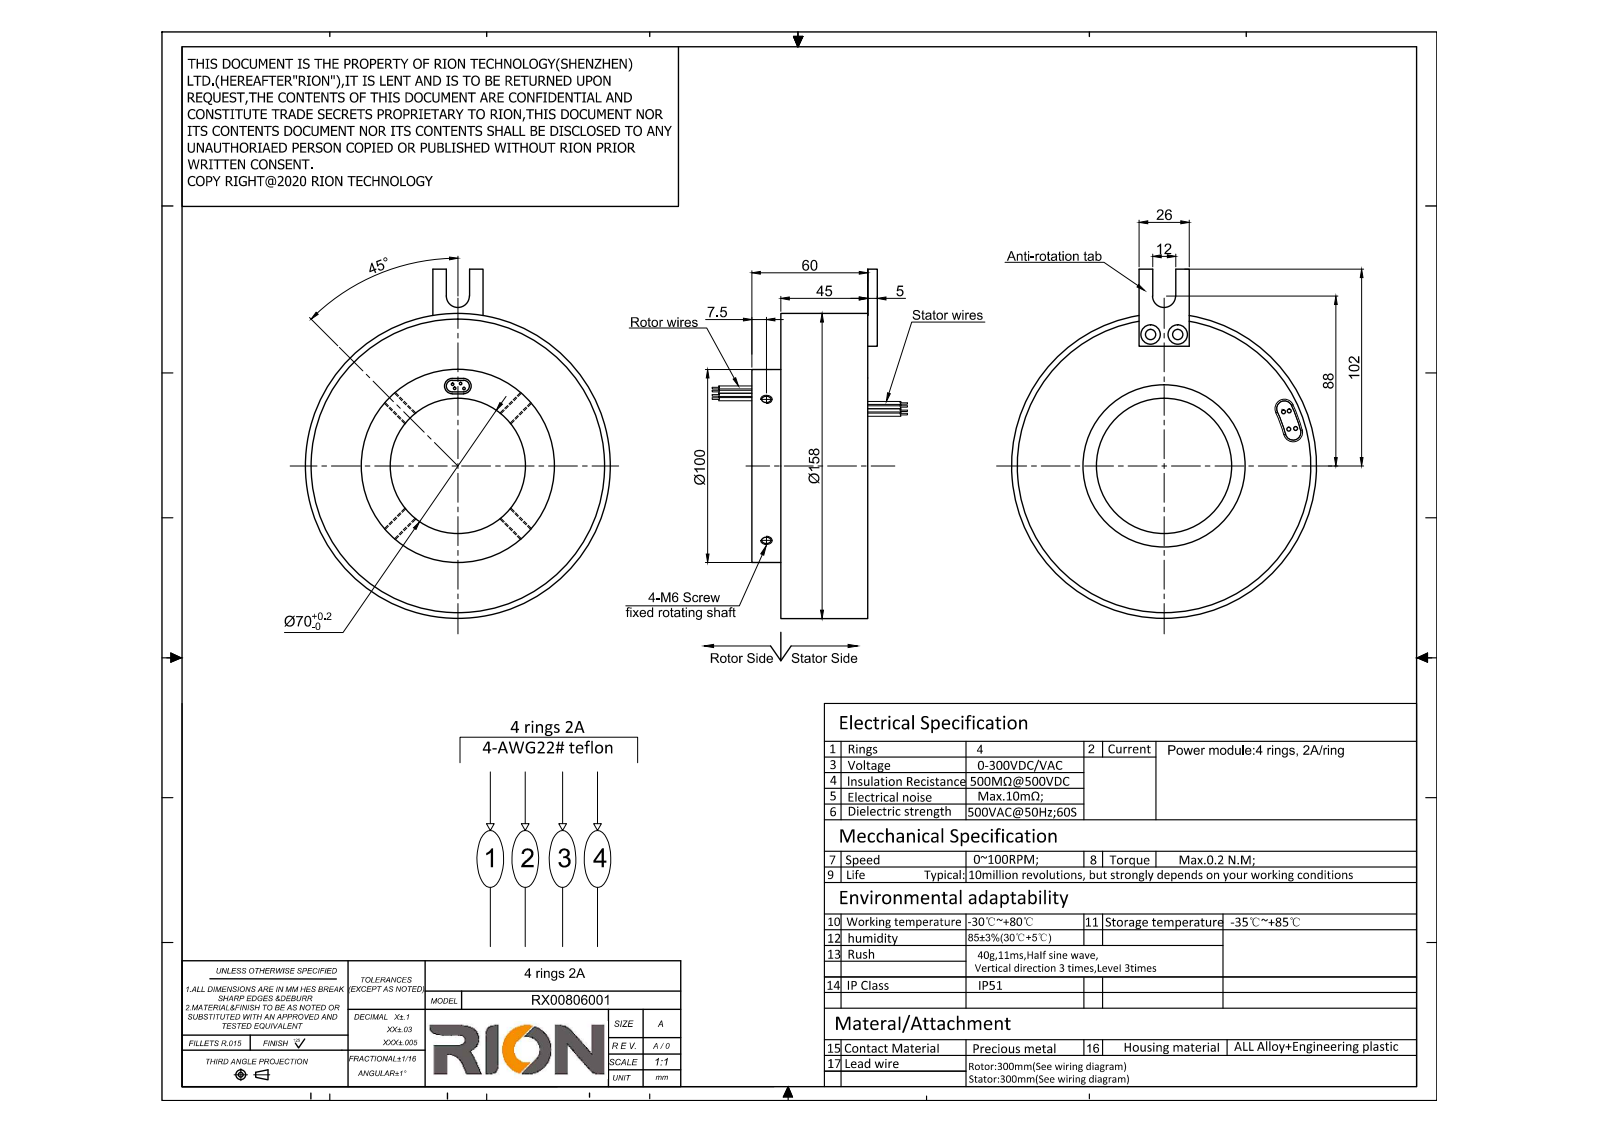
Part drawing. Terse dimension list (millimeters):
name: Admi3408C9B2ugze
written by: SIEMENS PLM Software NX 8.5 (AUTOMOTIVE_DESIGN)
unit: mm
bodies: 1 solid, 100 faces (33 planar, 59 cylindrical, 8 other)
size: 181 × 158 × 128
volume: 771 067 mm³; area: 83 600 mm²
holes: 6× ⌀5, 2× ⌀4.2, 1× ⌀70, 1× ⌀84.1, 1× ⌀152
bosses: 8× ⌀1.3, 1× ⌀158, 1× ⌀151.8, 1× ⌀100, 1× ⌀84
rounds: 2× R4, 2× R4.88, 1× R6, 1× R64.11, 1× R73.89
face distances: 45, 15, 60, 5, 65, 50, 1, 7, 26, 59
hole spacings: 68.36, 14
